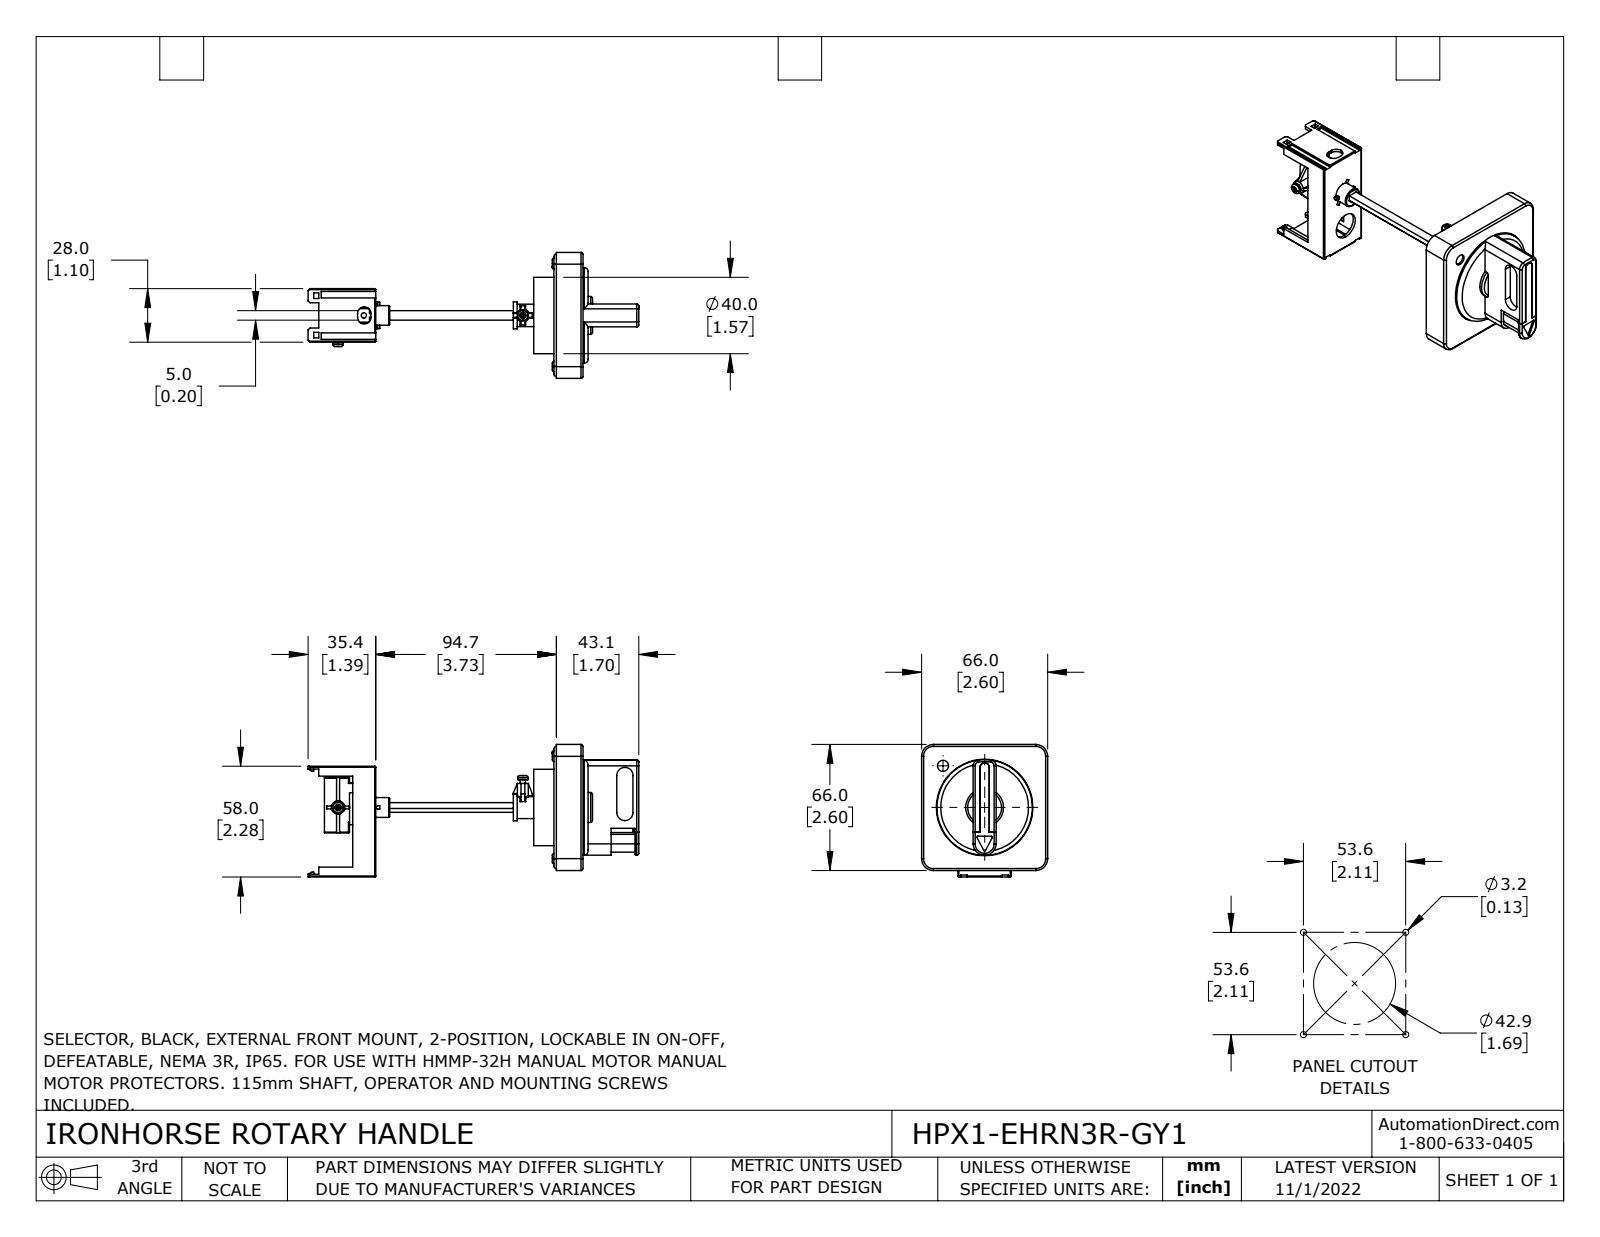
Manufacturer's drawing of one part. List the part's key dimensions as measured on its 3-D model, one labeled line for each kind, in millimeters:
Part name (STEP PRODUCT): HPX1-EHRN3R-GY1
STEP written by: SolidWorks 2021 (CONFIG_CONTROL_DESIGN)
Units: millimetres
Bodies: 3 solids, 774 faces (474 planar, 205 cylindrical, 95 other)
Overall size (bounding box): 173.2 × 69.4 × 66
Volume: 103 400 mm³ · Surface area: 39 540 mm²
Round holes (diameter × count): ⌀2.8 ×2, ⌀3.2 ×1, ⌀5.8 ×1, ⌀6.4 ×1, ⌀10.6 ×1, ⌀14 ×1, ⌀50.5 ×1
Round bosses / shafts (diameter × count): ⌀5.4 ×6, ⌀2.8 ×2, ⌀50 ×1, ⌀40 ×1, ⌀33.2 ×1, ⌀18 ×1, ⌀14 ×1, ⌀11.7 ×1
Partial cylindrical surfaces — rounded edges, fillets, slot ends (radius × count): R0.5 ×26, R0.2 ×24, R1 ×10, R3.5 ×7, R1.3 ×4, R3 ×4, R6.2 ×4, R0.3 ×2
Main face-to-face distances: 1.5, 13.9, 35.5, 30.5, 16.6, 39, 19, 26.5, 66, 27
Hole centre spacings: 3.7, 19.6, 22.7, 30.8, 46.8, 50.4
